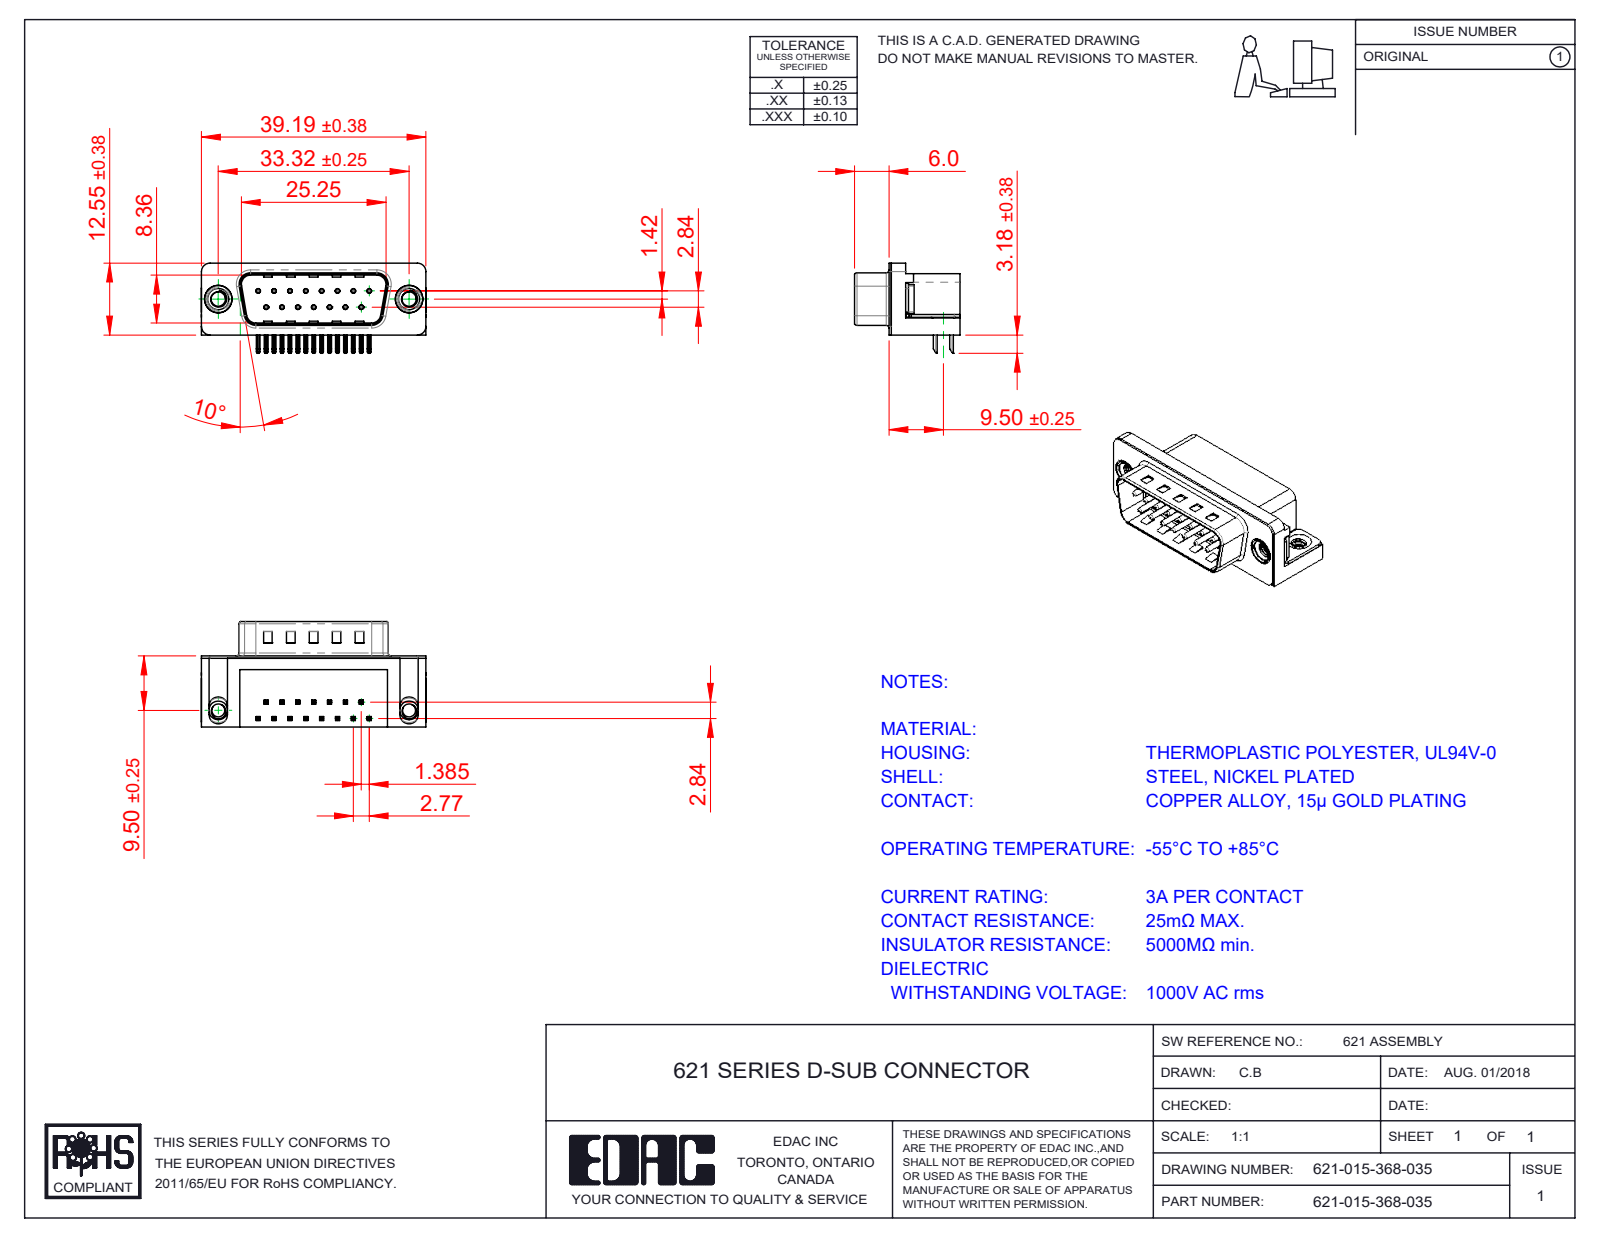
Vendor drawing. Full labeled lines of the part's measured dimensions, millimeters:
Part name (STEP PRODUCT): 621-015-368-035; 621 2 Prong Board Lock; 621 M3 Threaded Rivet; 621 Contact Top (+3 more)
STEP written by: SolidWorks 2016 (CONFIG_CONTROL_DESIGN)
Units: millimetres
Bodies: 21 solids, 1517 faces (925 planar, 457 cylindrical, 135 other)
Overall size (bounding box): 39.22 × 18.4 × 16.25
Volume: 4 409 mm³ · Surface area: 5 659 mm²
Round holes (diameter × count): ⌀0.35 ×15, ⌀0.8 ×15, ⌀2.5 ×2, ⌀4 ×2, ⌀4.8 ×2, ⌀5 ×2
Round bosses / shafts (diameter × count): ⌀0.75 ×15, ⌀4.9 ×2, ⌀4.75 ×2, ⌀3.9 ×2
Partial cylindrical surfaces — rounded edges, fillets, slot ends (radius × count): R0.25 ×68, R0.12 ×30, R1 ×16, R0.5 ×14, R1.6 ×8, R1.5 ×6, R0.32 ×4, R0.9 ×4
Main face-to-face distances: 0.4, 12, 10.35, 2.1, 10.46, 12.4, 1.7, 10.86, 8.76, 9.5
Hole centre spacings: 3.16, 2.77, 5.54, 8.31, 11.08, 5.03, 5.04, 7.48
